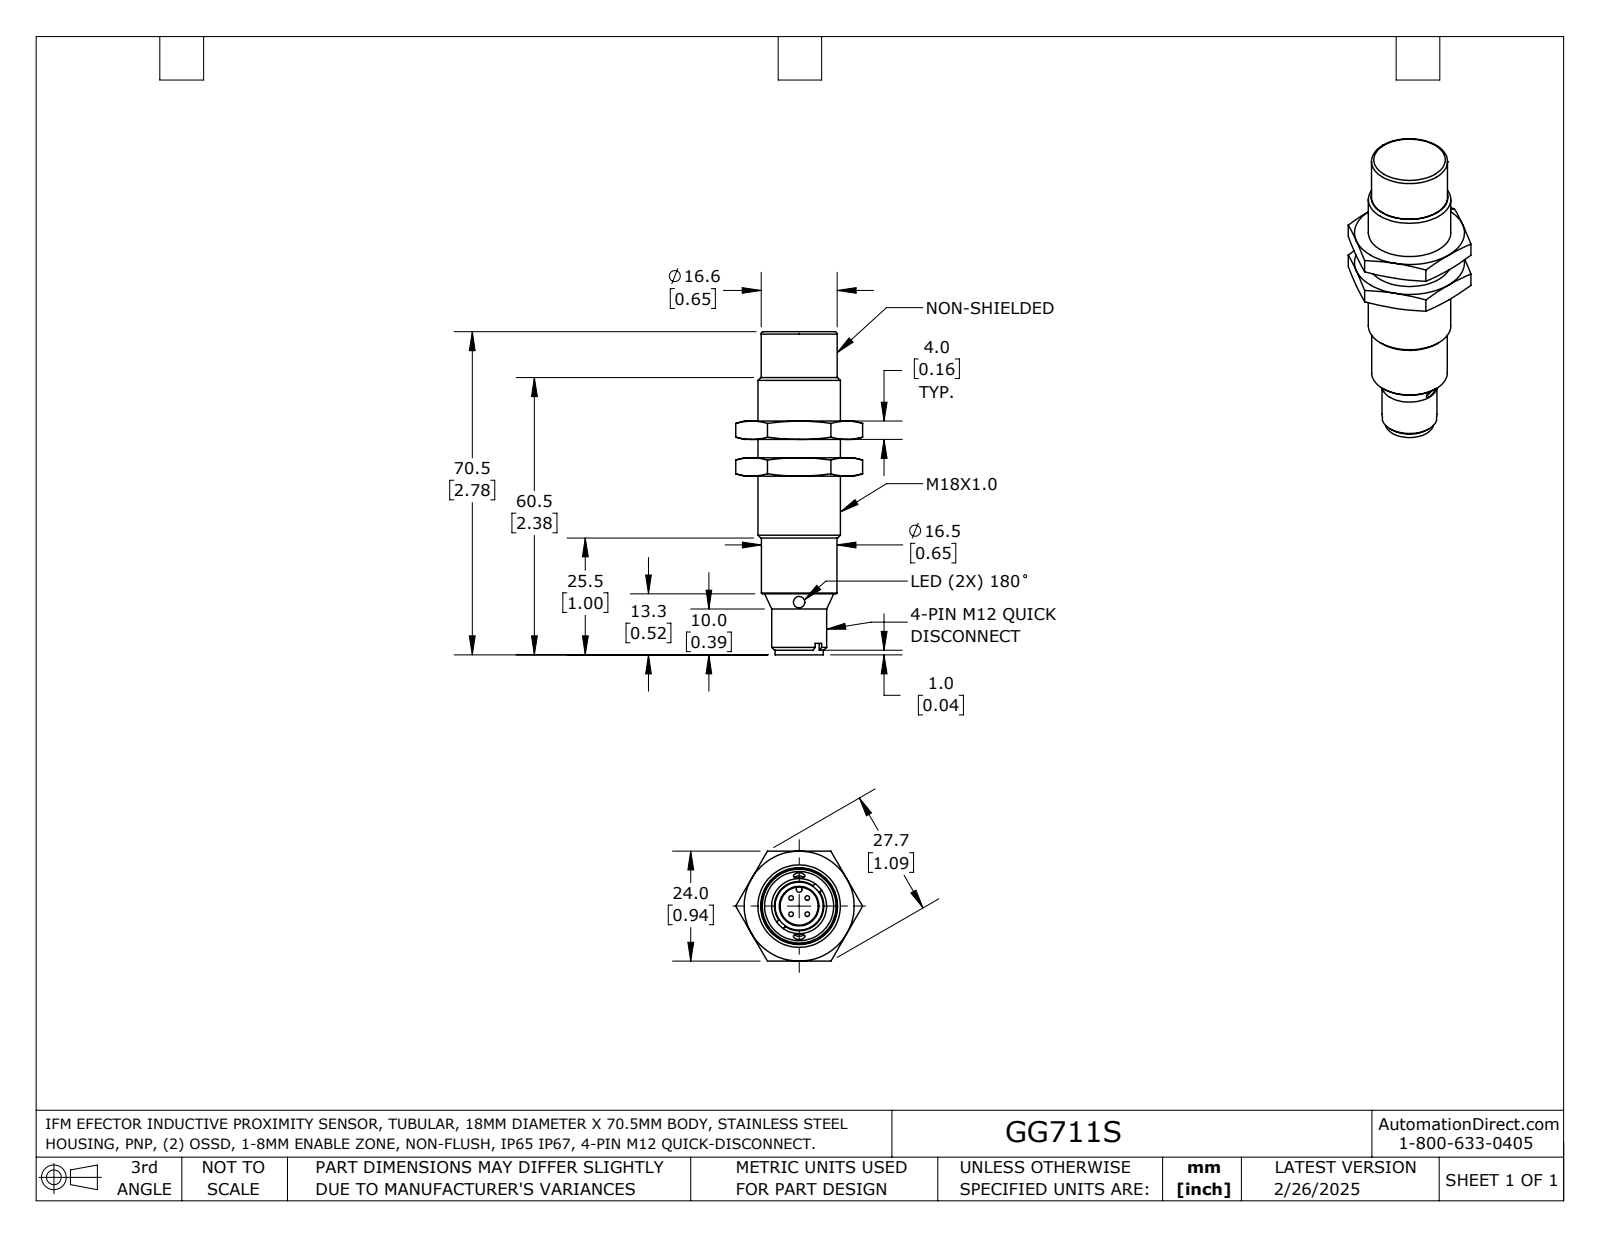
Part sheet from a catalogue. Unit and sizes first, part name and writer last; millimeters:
Units: millimetres
Overall size (bounding box): 70.5 × 27.71 × 24
Round holes (diameter × count): ⌀2.5 ×1, ⌀8.3 ×1, ⌀16.92 ×1
Round bosses / shafts (diameter × count): ⌀18 ×1, ⌀16.6 ×1, ⌀16.5 ×1, ⌀12 ×1, ⌀10.5 ×1
Partial cylindrical surfaces — rounded edges, fillets, slot ends (radius × count): R0.6 ×1
Main face-to-face distances: 4, 8, 24, 12, 31.5, 27.5, 23.5, 19.5, 30.2, 34.2
Volume: 16 885 mm³ · Surface area: 6 358 mm²
Bodies: 3 solids, 113 faces (33 planar, 22 cylindrical, 58 other)
Part name (STEP PRODUCT): GG711S
STEP written by: SolidWorks 2024 (AUTOMOTIVE_DESIGN)
